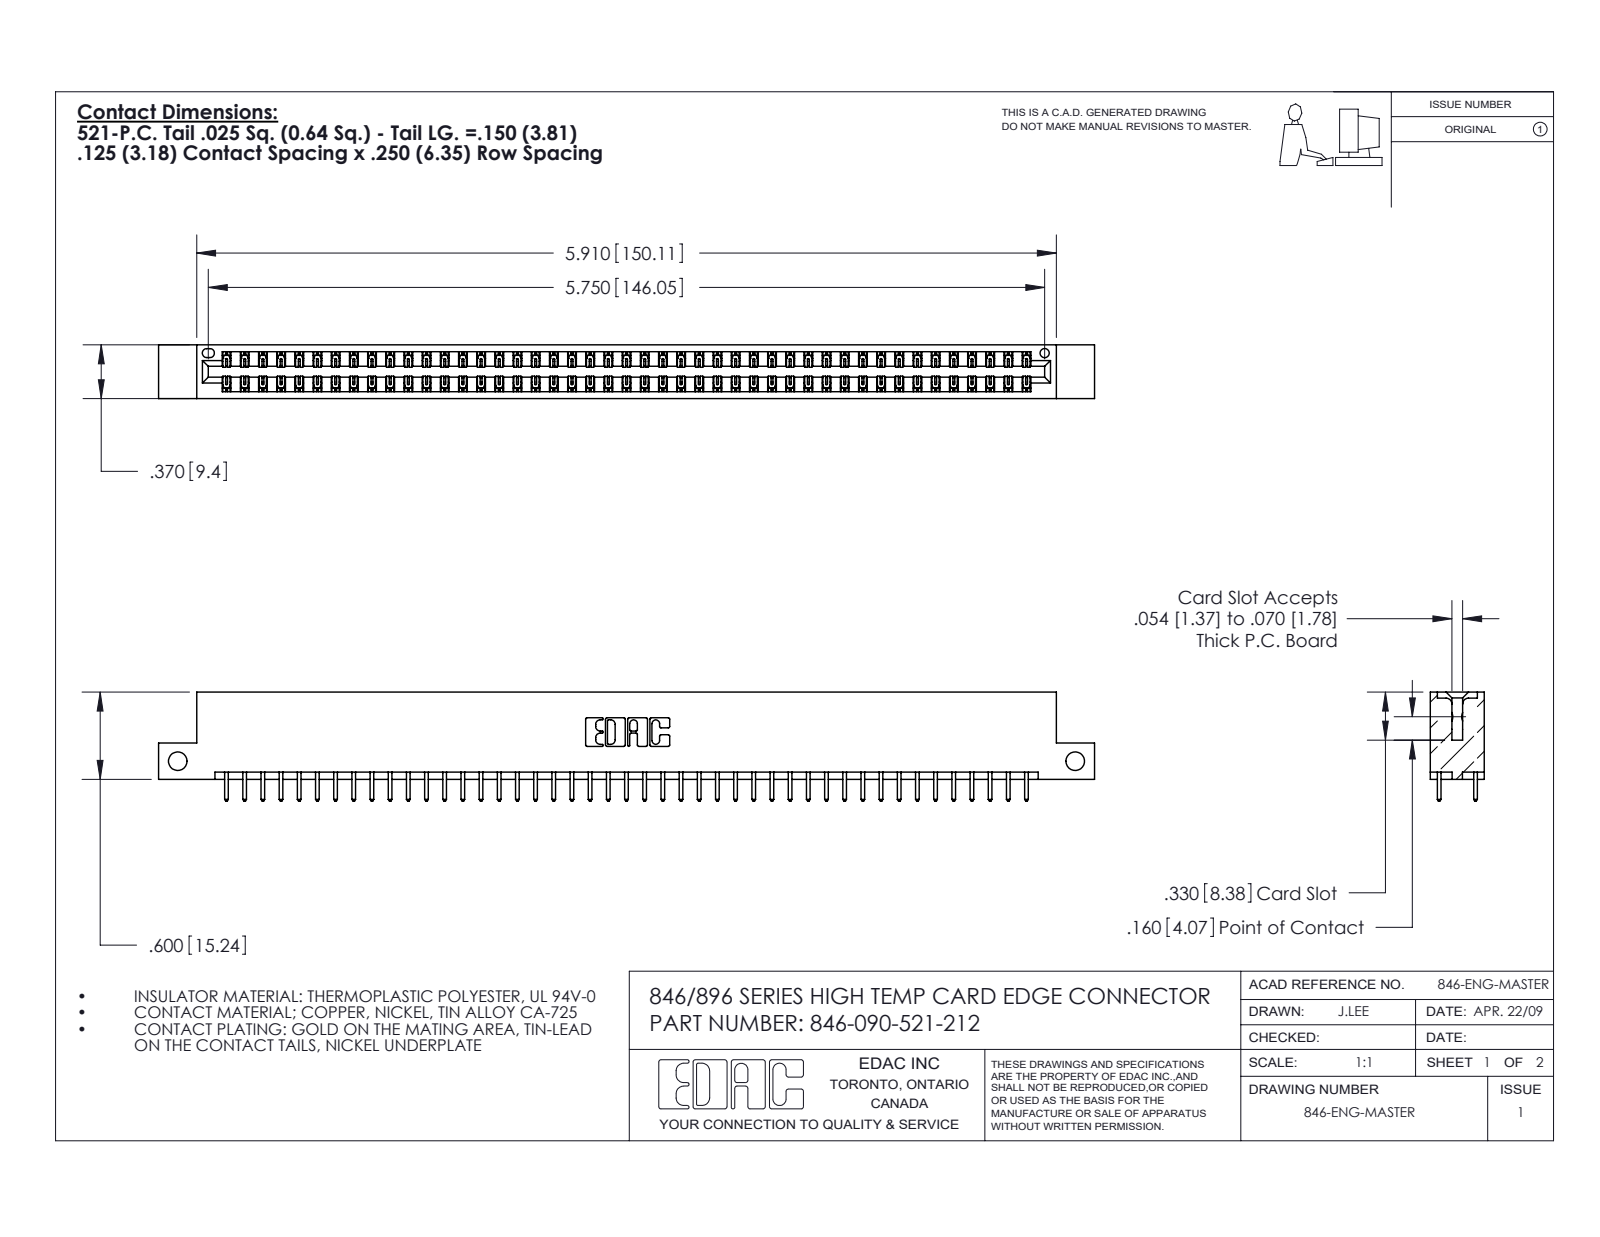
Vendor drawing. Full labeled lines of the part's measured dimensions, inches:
Part name (STEP PRODUCT): 345-292-001_345-293-121; 346-090-521-212; 346 Part_Flush Mounting Lugs - Side Mount
STEP written by: SolidWorks 2016 (CONFIG_CONTROL_DESIGN)
Units: inches
Bodies: 91 solids, 4802 faces (3226 planar, 1576 cylindrical, 0 other)
Overall size (bounding box): 6.435 × 0.75 × 0.37
Volume: 0.966 in³ · Surface area: 33.22 in²
Round holes (diameter × count): ⌀0.128 ×2, ⌀0.064 ×1
Partial cylindrical surfaces — rounded edges, fillets, slot ends (radius × count): R0.006 ×135, R0.01 ×90, R0.01 ×22, R0.007 ×6, R0.031 ×6, R0.026 ×3, R0.014 ×2, R0.022 ×2
Main face-to-face distances: 0.048, 0.322, 0.25, 0.37, 0.072, 0.298, 0.025, 0.275, 0.148, 0.222
Hole centre spacings: 6.17
